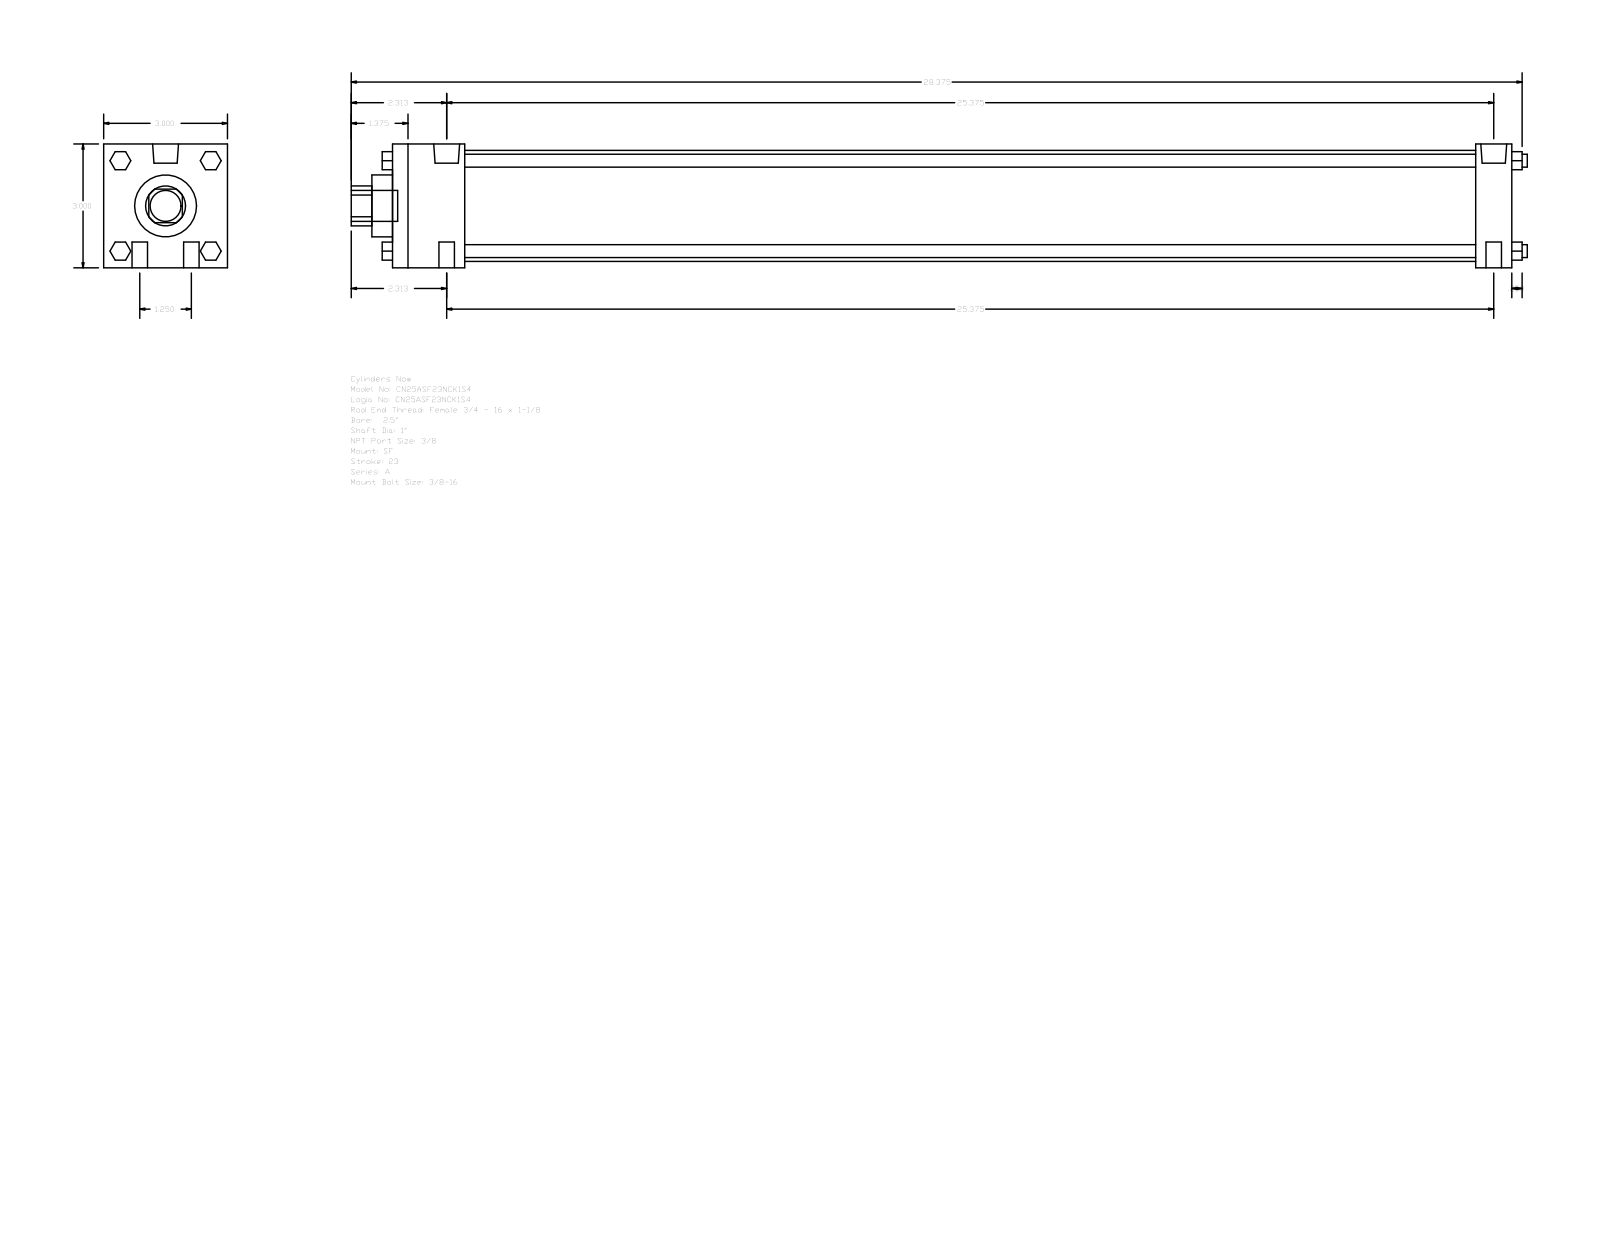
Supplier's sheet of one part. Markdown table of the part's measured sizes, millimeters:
| quantity | value |
| --- | --- |
| part name | A_SF__0250_1 |
| STEP written by | GSSL Pune (CONFIG_CONTROL_DESIGN) |
| units | millimeters |
| bodies | 0 solids, 124 faces (94 planar, 30 cylindrical, 0 other) |
| overall size | 723.9 × 76.2 × 76.2 |
| round holes (diameter × count) | 25.4 × 1, 38.1 × 1, 68.33 × 1 |
| round bosses / shafts (diameter × count) | 9.53 × 4, 7.94 × 4, 15.93 × 2, 5.56 × 2, 19.05 × 1 |
| partial cylindrical surfaces (radius × count) | 12.29 × 1 |
| main face-to-face distances | 76.2, 688.98, 666.75, 22.23, 44.45, 622.3, 644.53, 12.7, 701.68, 6.35 |
